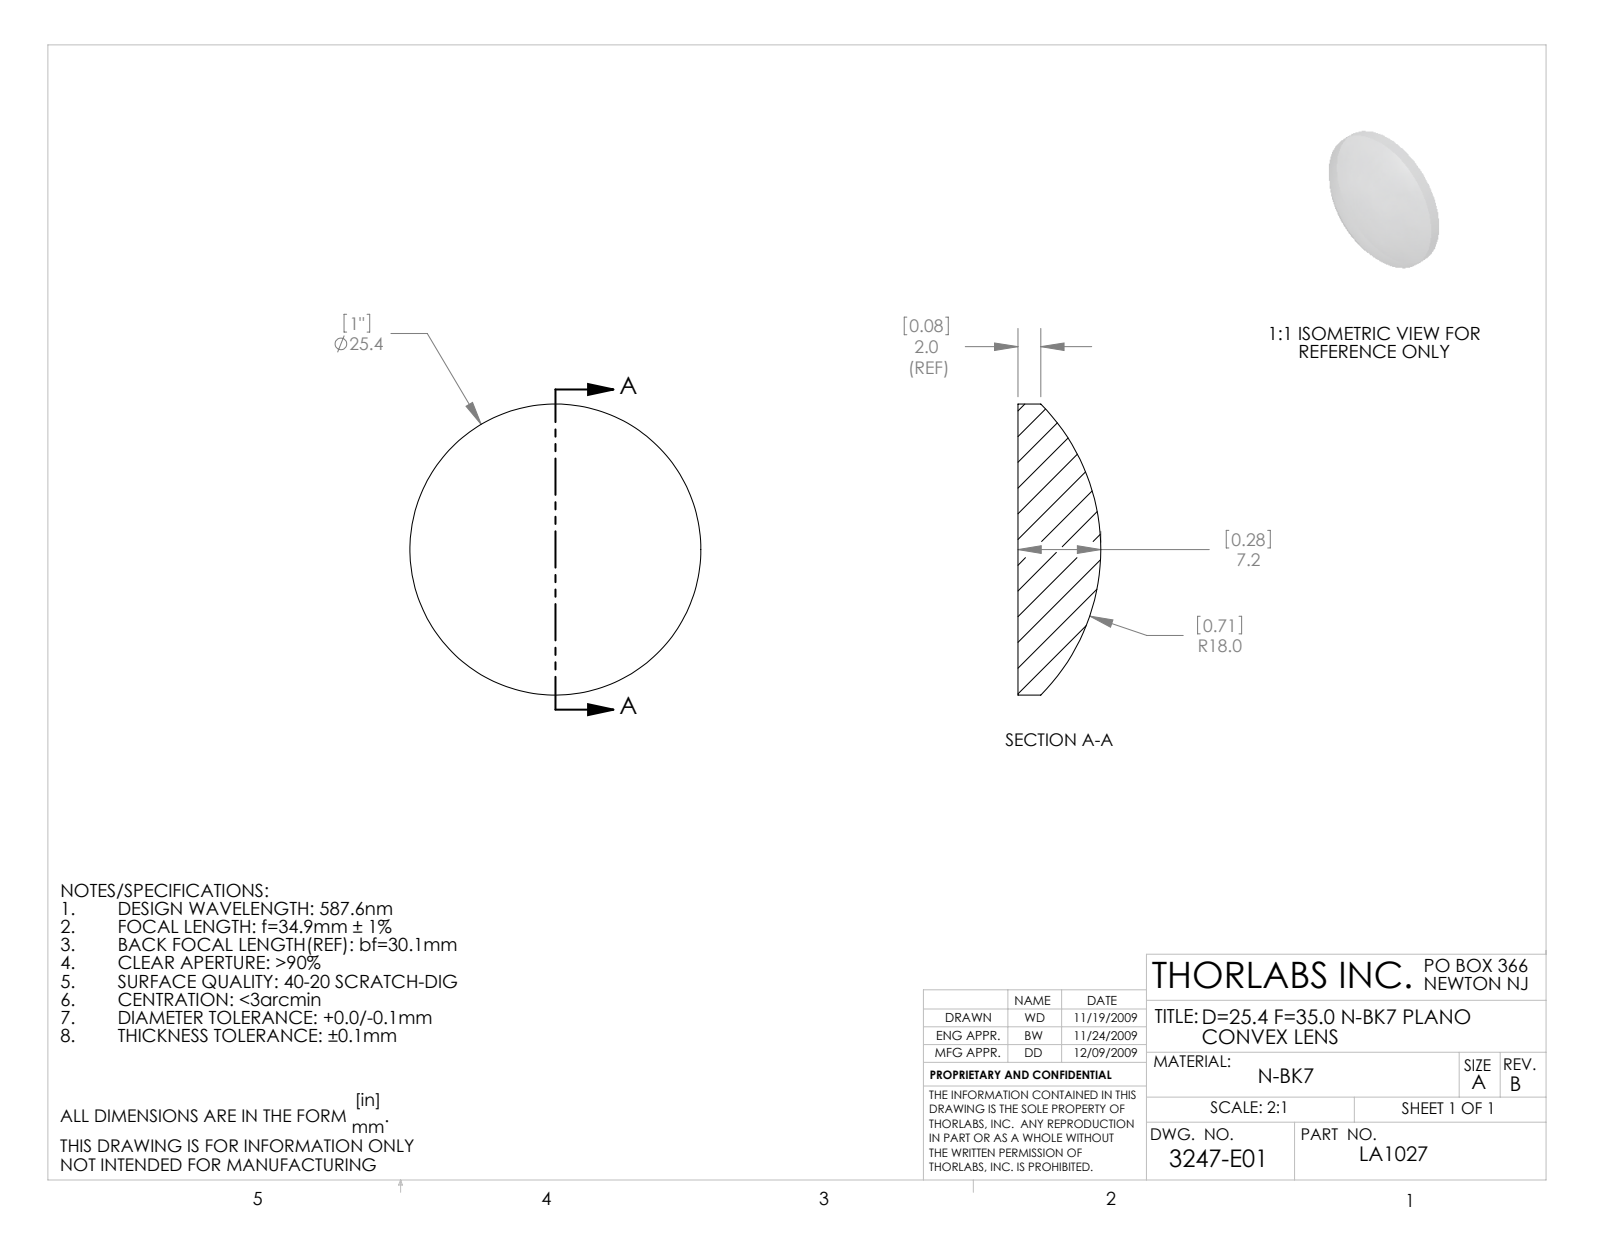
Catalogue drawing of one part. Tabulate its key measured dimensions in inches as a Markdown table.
| quantity | value |
| --- | --- |
| part name | 3247-E0W |
| STEP written by | SolidWorks 2009 (AUTOMOTIVE_DESIGN) |
| units | inches |
| bodies | 1 solid, 5 faces (1 planar, 2 cylindrical, 2 other) |
| overall size | 1 × 1 × 0.285 |
| volume | 0.147 in³ |
| surface area | 1.951 in² |
| round bosses / shafts (diameter × count) | 1 × 1 |
